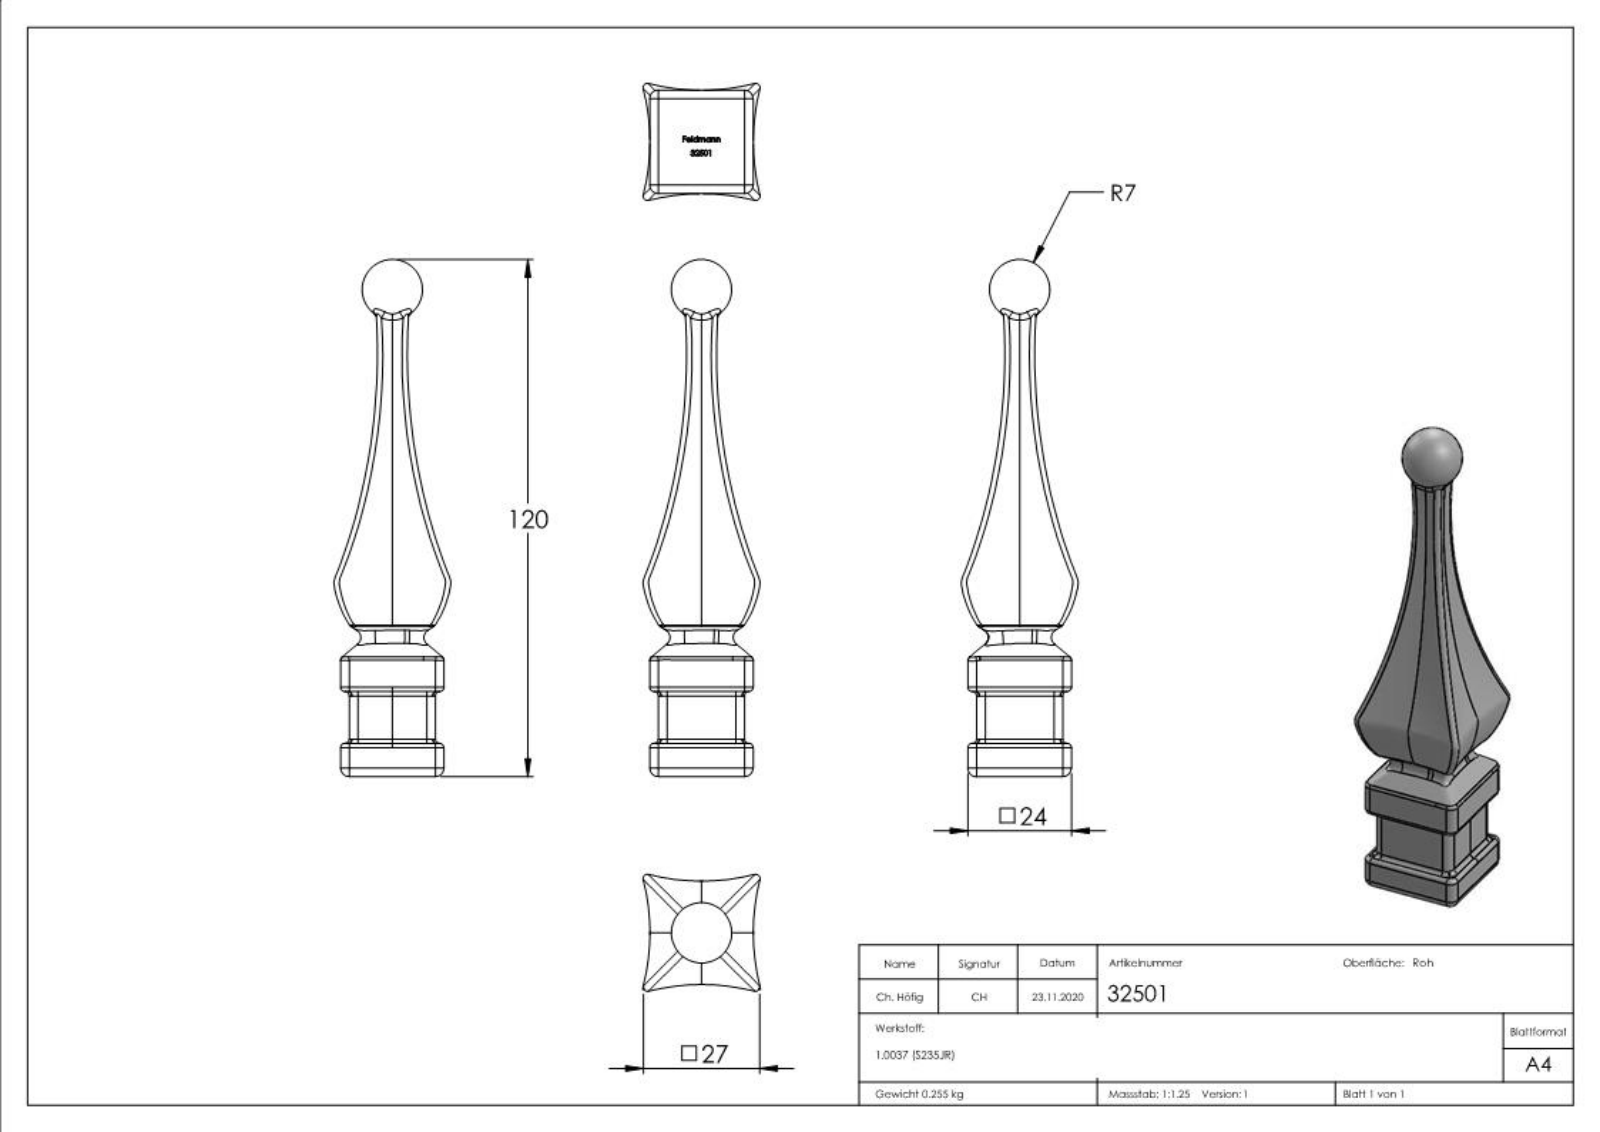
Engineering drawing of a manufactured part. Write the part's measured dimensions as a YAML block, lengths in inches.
part_name: "32501"
step_written_by: "SolidWorks 2018 (CONFIG_CONTROL_DESIGN)"
units: inches
bodies: {solids: 1, faces: 381, planar: 130, cylindrical: 36, other: 215}
overall_size: [4.724, 1.069, 1.069]
volume: 1.997
surface_area: 13.27
partial_cylinders:
  - {radius: 0.039, count: 16}
  - {radius: 0.079, count: 12}
face_to_face_distances: [0.079, 0.866, 0.945, 0.787, 0.472, 0.305, 0.778, 0.301, 0.774, 0.394]
